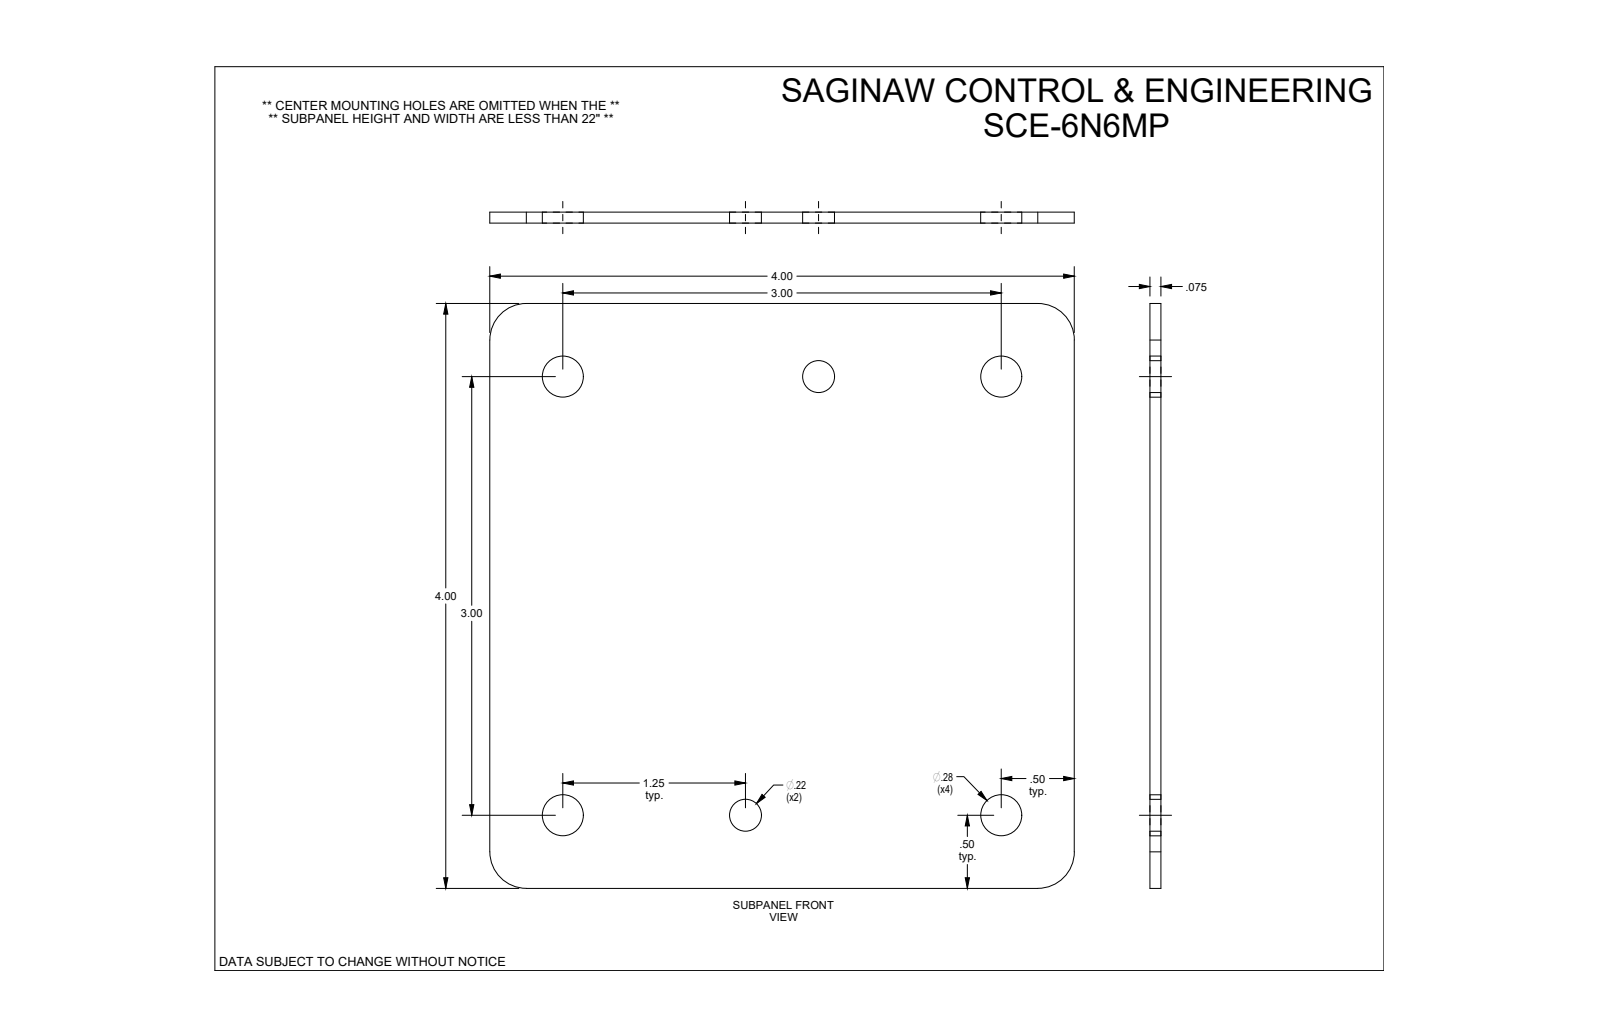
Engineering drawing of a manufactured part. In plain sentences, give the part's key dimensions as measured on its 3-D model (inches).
The part is named "SCE-6N6MP". Its 3-D file was written by "SolidWorks 2019 (CONFIG_CONTROL_DESIGN)". It is 1 solid with 16 faces: 6 planar, 10 cylindrical and 0 other. Overall it measures 4 by 4 by 0.075 inches. Its volume is 1.172 cubic inches and its surface area 32.78 square inches. Round holes: 4 of diameter 0.281, 2 of diameter 0.218. Partial cylindrical surfaces (rounded edges, fillets, slot ends): 4 of radius 0.25. The main face-to-face distances are 0.075, 4. The hole center spacings are 3, 1.25, 1.75, 3.25, 3.473, 4.243, 3.041.
